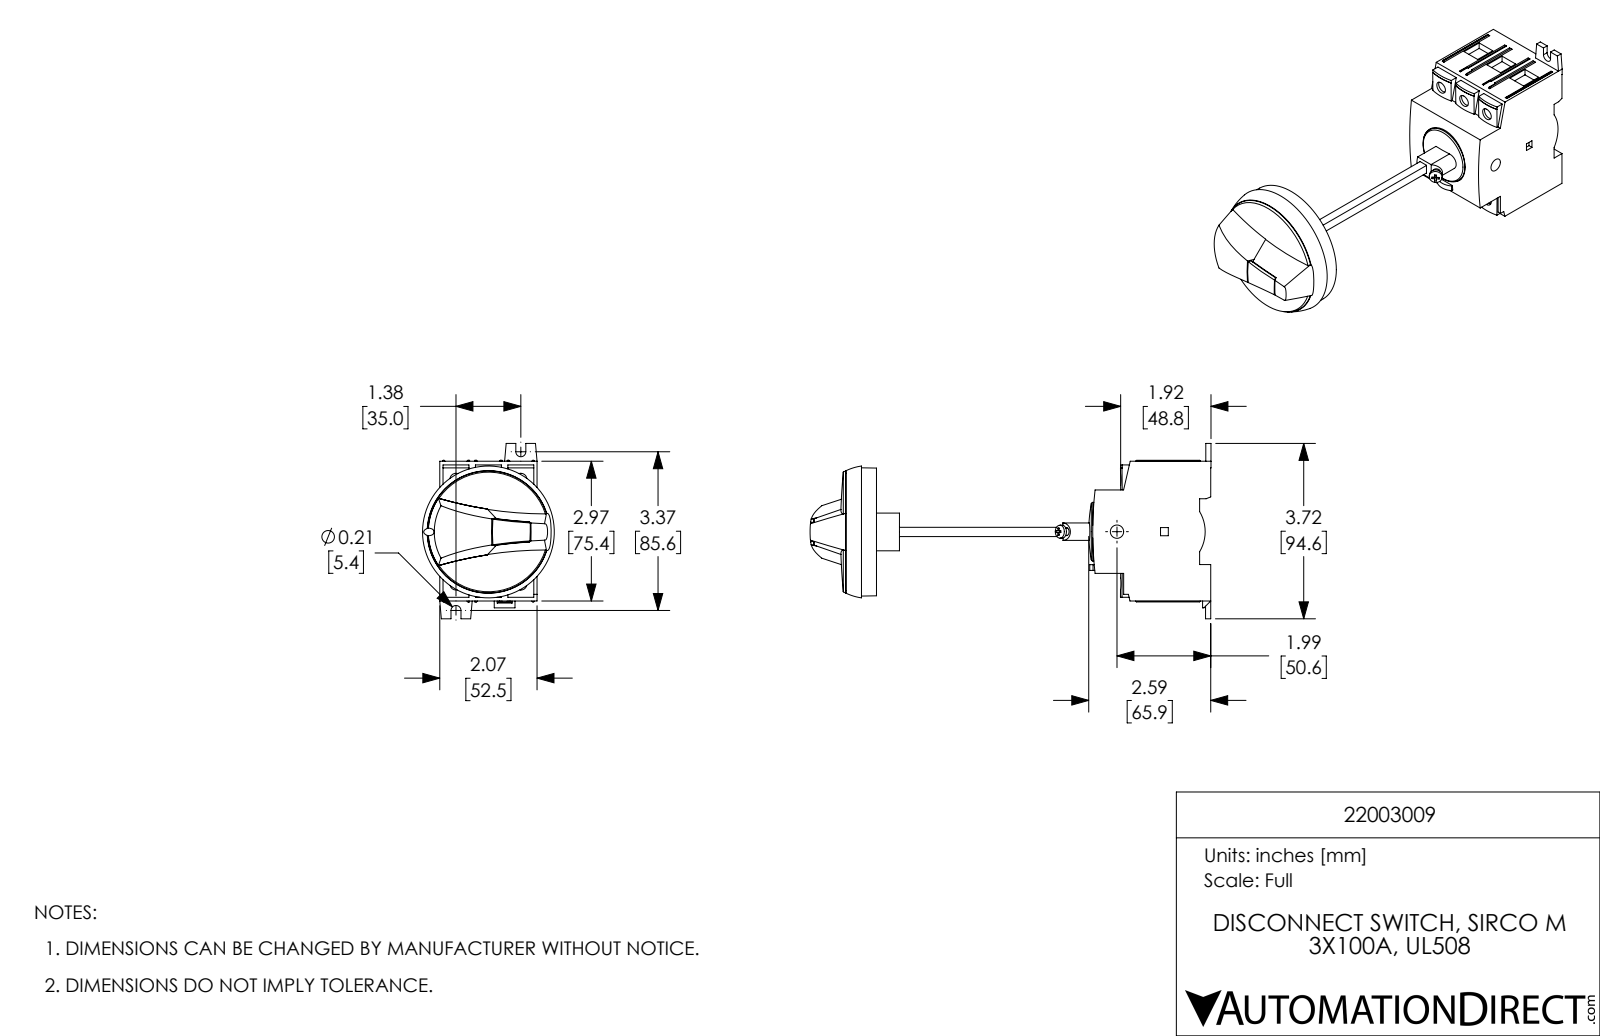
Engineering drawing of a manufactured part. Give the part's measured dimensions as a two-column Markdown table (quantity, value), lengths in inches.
| quantity | value |
| --- | --- |
| part name | 22003009 |
| STEP written by | SolidWorks 2017 (AUTOMOTIVE_DESIGN) |
| units | inches |
| bodies | 6 solids, 371 faces (256 planar, 64 cylindrical, 51 other) |
| overall size | 8.52 × 3.724 × 2.8 |
| volume | 18.79 in³ |
| surface area | 75.93 in² |
| round holes (diameter × count) | 0.26 × 6, 0.169 × 4, 0.283 × 1, 0.457 × 1, 1.26 × 1, 2.618 × 1 |
| round bosses / shafts (diameter × count) | 1.244 × 1, 0.801 × 1, 0.276 × 1, 0.157 × 1, 0.066 × 1 |
| partial cylindrical surfaces (radius × count) | 1.18 × 9, 0.012 × 4, 0.106 × 2, 0.37 × 1, 0.728 × 1, 0.827 × 1, 7.862 × 1 |
| main face-to-face distances | 2.067, 7.132, 2.969, 0.197, 0.935, 1.132, 0.587, 2.391, 4.742, 0.793 |
| hole center spacings | 0.689, 0.961, 1.307, 2.325, 2.22, 0.346, 0.356, 0.636 |
